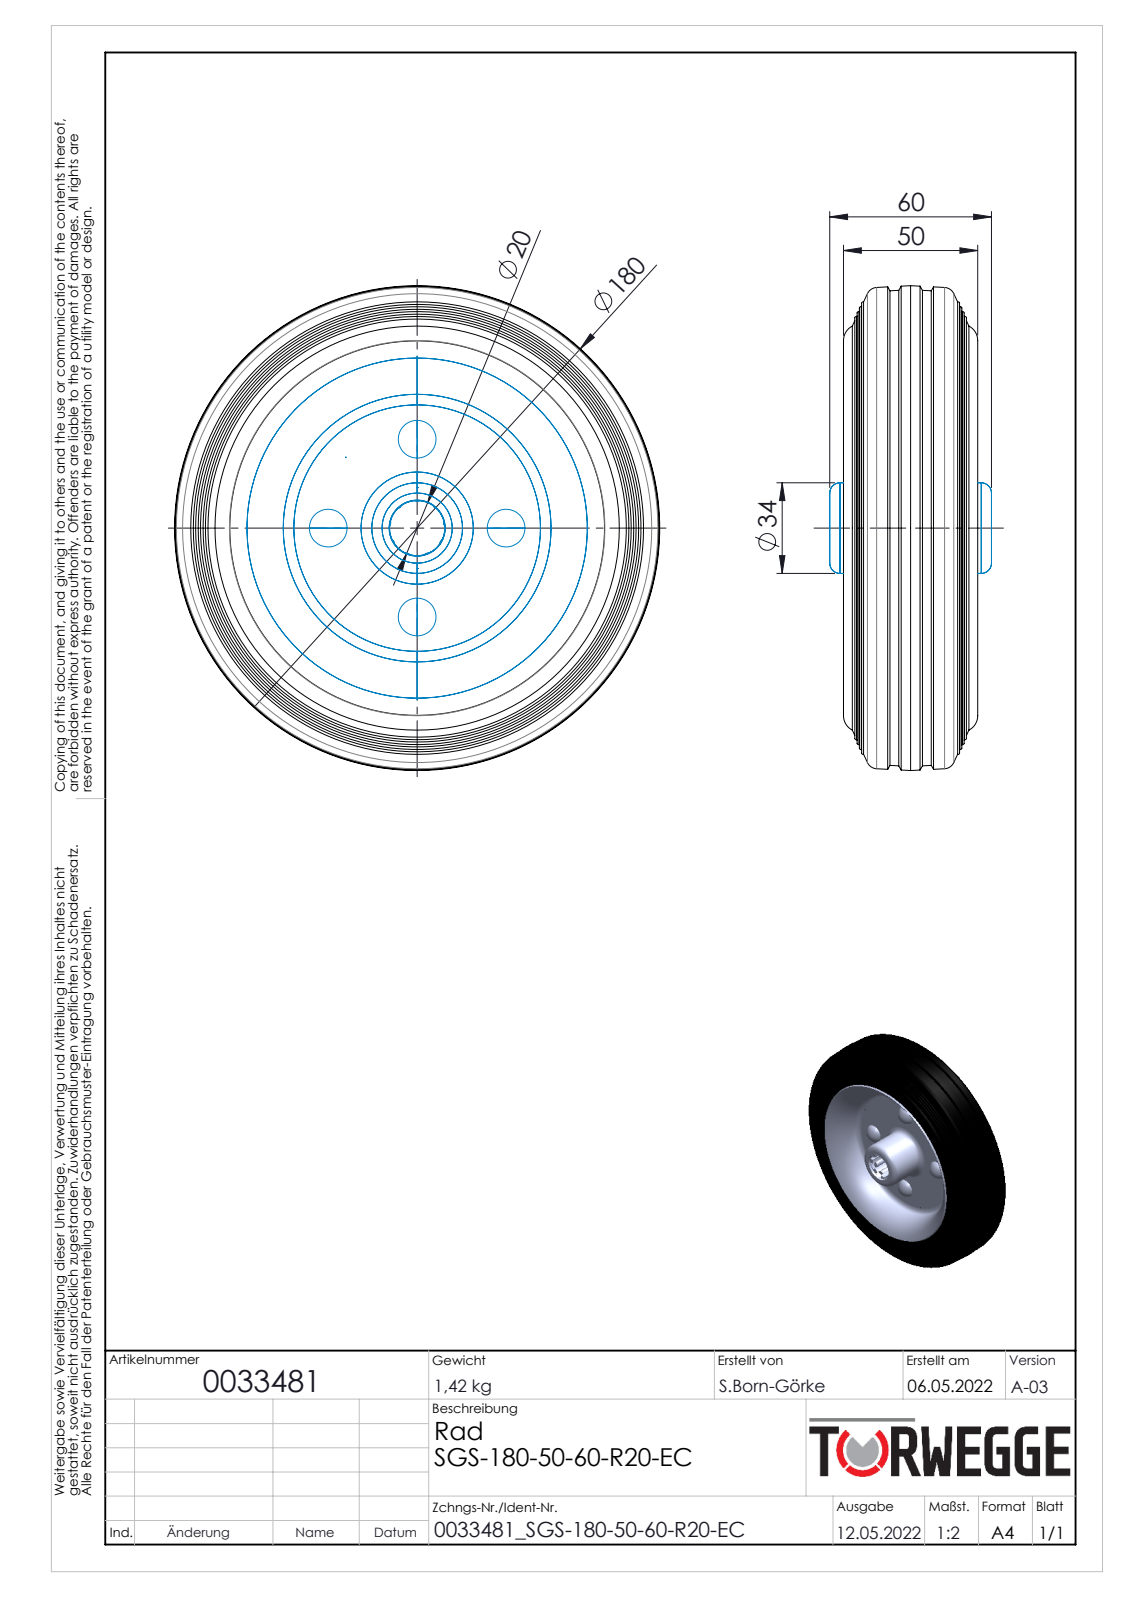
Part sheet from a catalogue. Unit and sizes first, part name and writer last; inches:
Units: inches
Overall size (bounding box): 7.087 × 7.087 × 2.362
Round bosses / shafts (diameter × count): ⌀1.325 ×1, ⌀1.183 ×1, ⌀0.819 ×1, ⌀0.807 ×1
Partial cylindrical surfaces — rounded edges, fillets, slot ends (radius × count): R0.098 ×9, R0.502 ×1
Main face-to-face distances: 0.142, 0.136, 0.953, 1.094, 1.039, 0.157, 1.11, 1.252, 2.205, 0.071
Bodies: 0 solids, 239 faces (78 planar, 51 cylindrical, 110 other)
Part name (STEP PRODUCT): 0033481
STEP written by: SolidWorks 2020 (AUTOMOTIVE_DESIGN)
